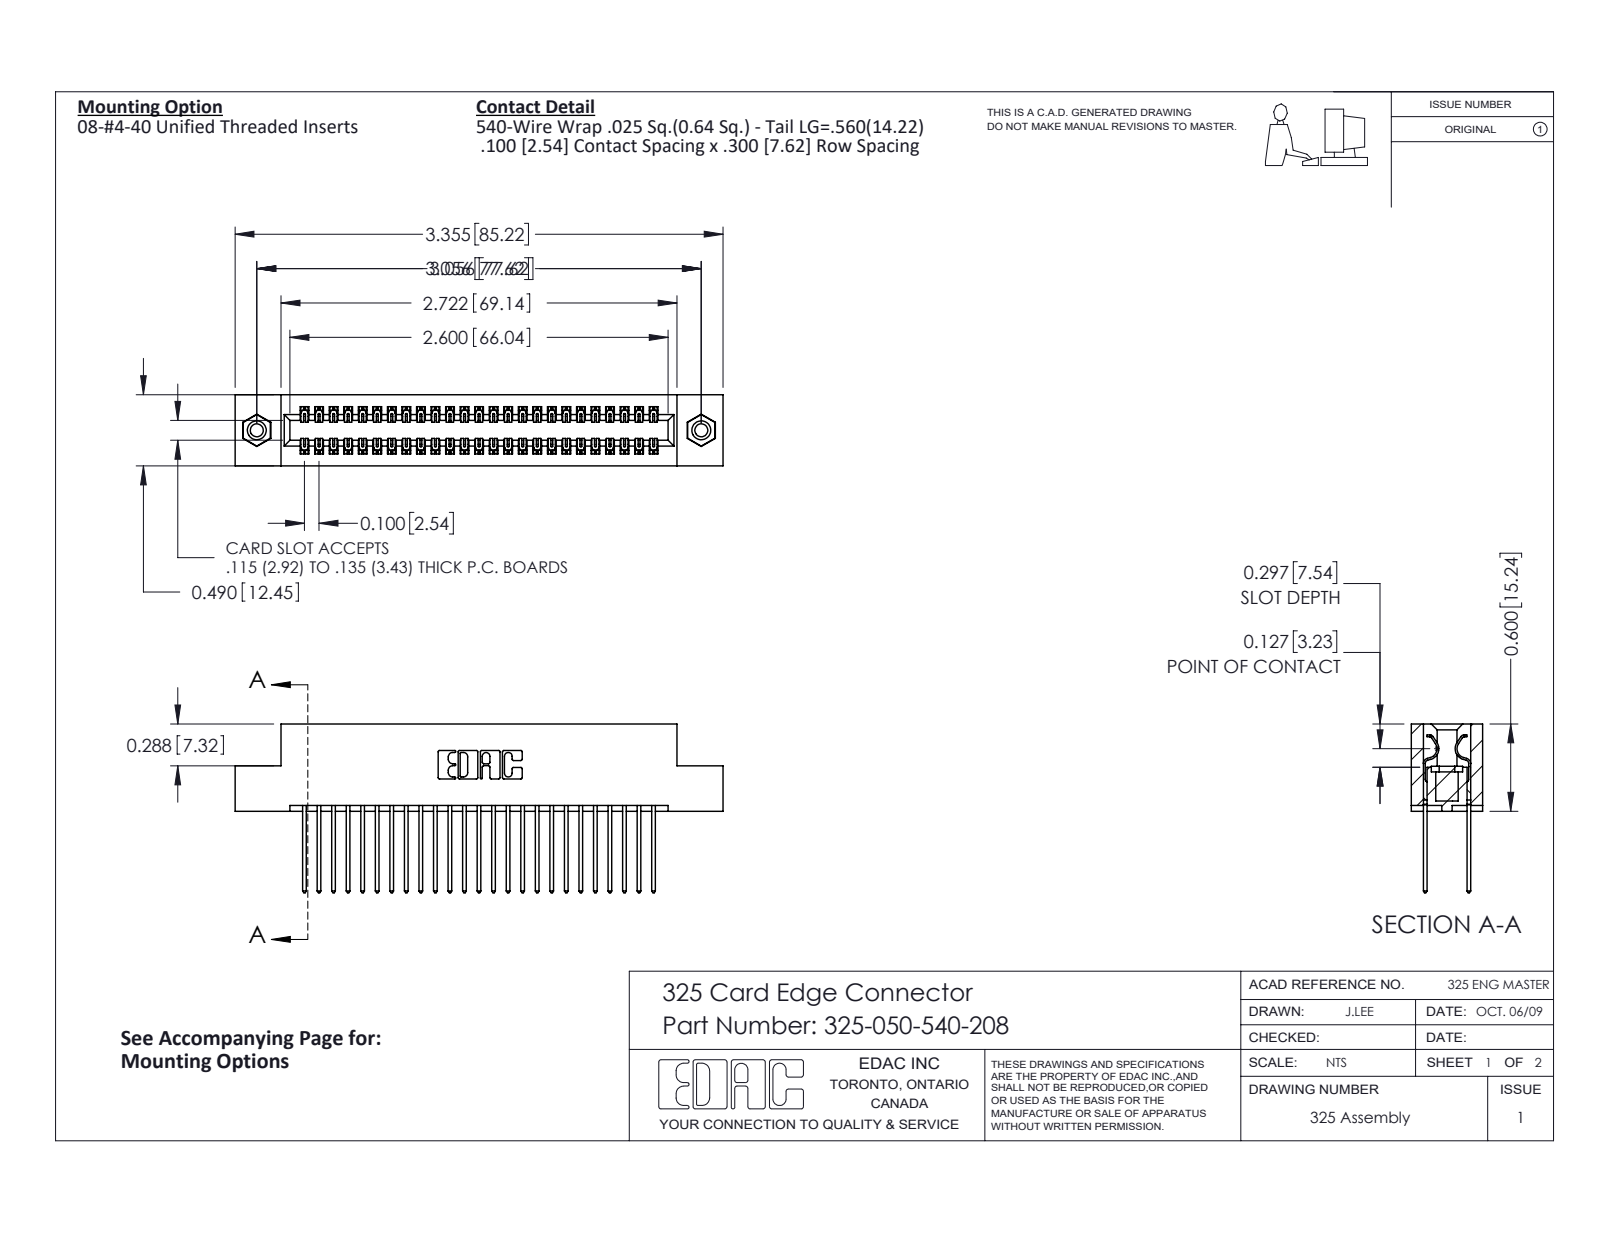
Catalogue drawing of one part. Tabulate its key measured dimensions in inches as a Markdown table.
| quantity | value |
| --- | --- |
| part name | 325-050-540-208; 345-250-001_345-250-003-102; 325 Part_TI; 325-292-001_325-293-140 |
| STEP written by | SolidWorks 2016 (CONFIG_CONTROL_DESIGN) |
| units | inches |
| bodies | 53 solids, 2774 faces (1902 planar, 856 cylindrical, 16 other) |
| overall size | 3.355 × 1.16 × 0.49 |
| volume | 0.673 in³ |
| surface area | 21.49 in² |
| round holes (diameter × count) | 0.089 × 2, 0.125 × 2, 0.16 × 2 |
| round bosses / shafts (diameter × count) | 0.155 × 2 |
| partial cylindrical surfaces (radius × count) | 0.006 × 75, 0.01 × 50, 0.01 × 22, 0.007 × 6, 0.031 × 6, 0.026 × 3, 0.014 × 2, 0.022 × 2 |
| main face-to-face distances | 0.083, 0.407, 0.3, 0.107, 0.383, 0.025, 0.49, 0.325, 0.275, 0.04 |
| hole center spacings | 3.056 |
